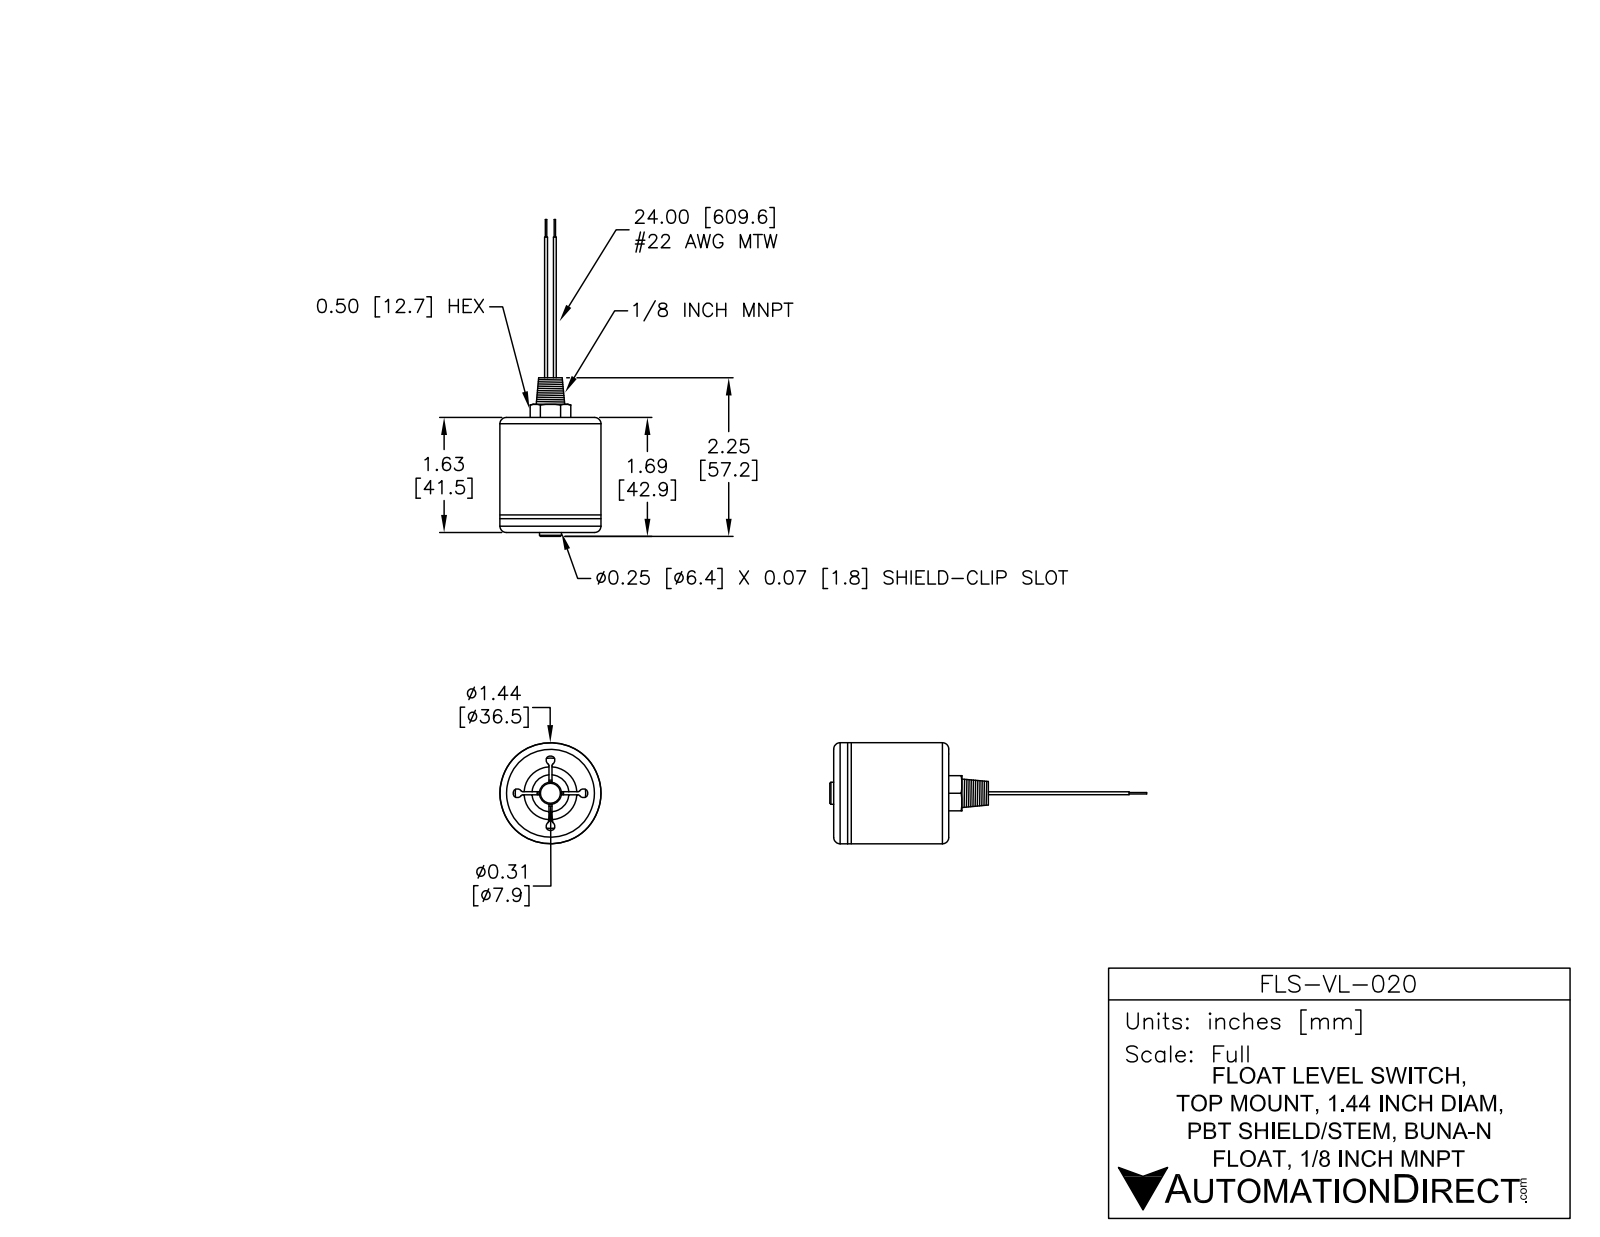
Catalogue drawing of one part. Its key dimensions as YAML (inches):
part_name: "FLS-VL-020"
step_written_by: "SolidWorks 2013 (AUTOMOTIVE_DESIGN)"
units: inches
bodies: {solids: 2, faces: 125, planar: 53, cylindrical: 54, other: 18}
overall_size: [4.984, 1.437, 1.437]
volume: 0.782
surface_area: 23.17
round_holes:
  - {diameter: 0.125, count: 4}
  - {diameter: 1.312, count: 1}
  - {diameter: 1.393, count: 1}
round_bosses_or_shafts:
  - {diameter: 0.04, count: 4}
  - {diameter: 0.02, count: 2}
  - {diameter: 1.437, count: 1}
  - {diameter: 0.873, count: 1}
  - {diameter: 0.313, count: 1}
  - {diameter: 0.313, count: 1}
  - {diameter: 0.25, count: 1}
partial_cylinders:
  - {radius: 0.164, count: 2}
face_to_face_distances: [1.508, 1.477, 0.031, 0.11, 1.587, 1.618, 1.493, 1.383, 0.094, 0.125]
hole_center_spacings: [0.5, 0.707, 1, 0.5, 0.5]
